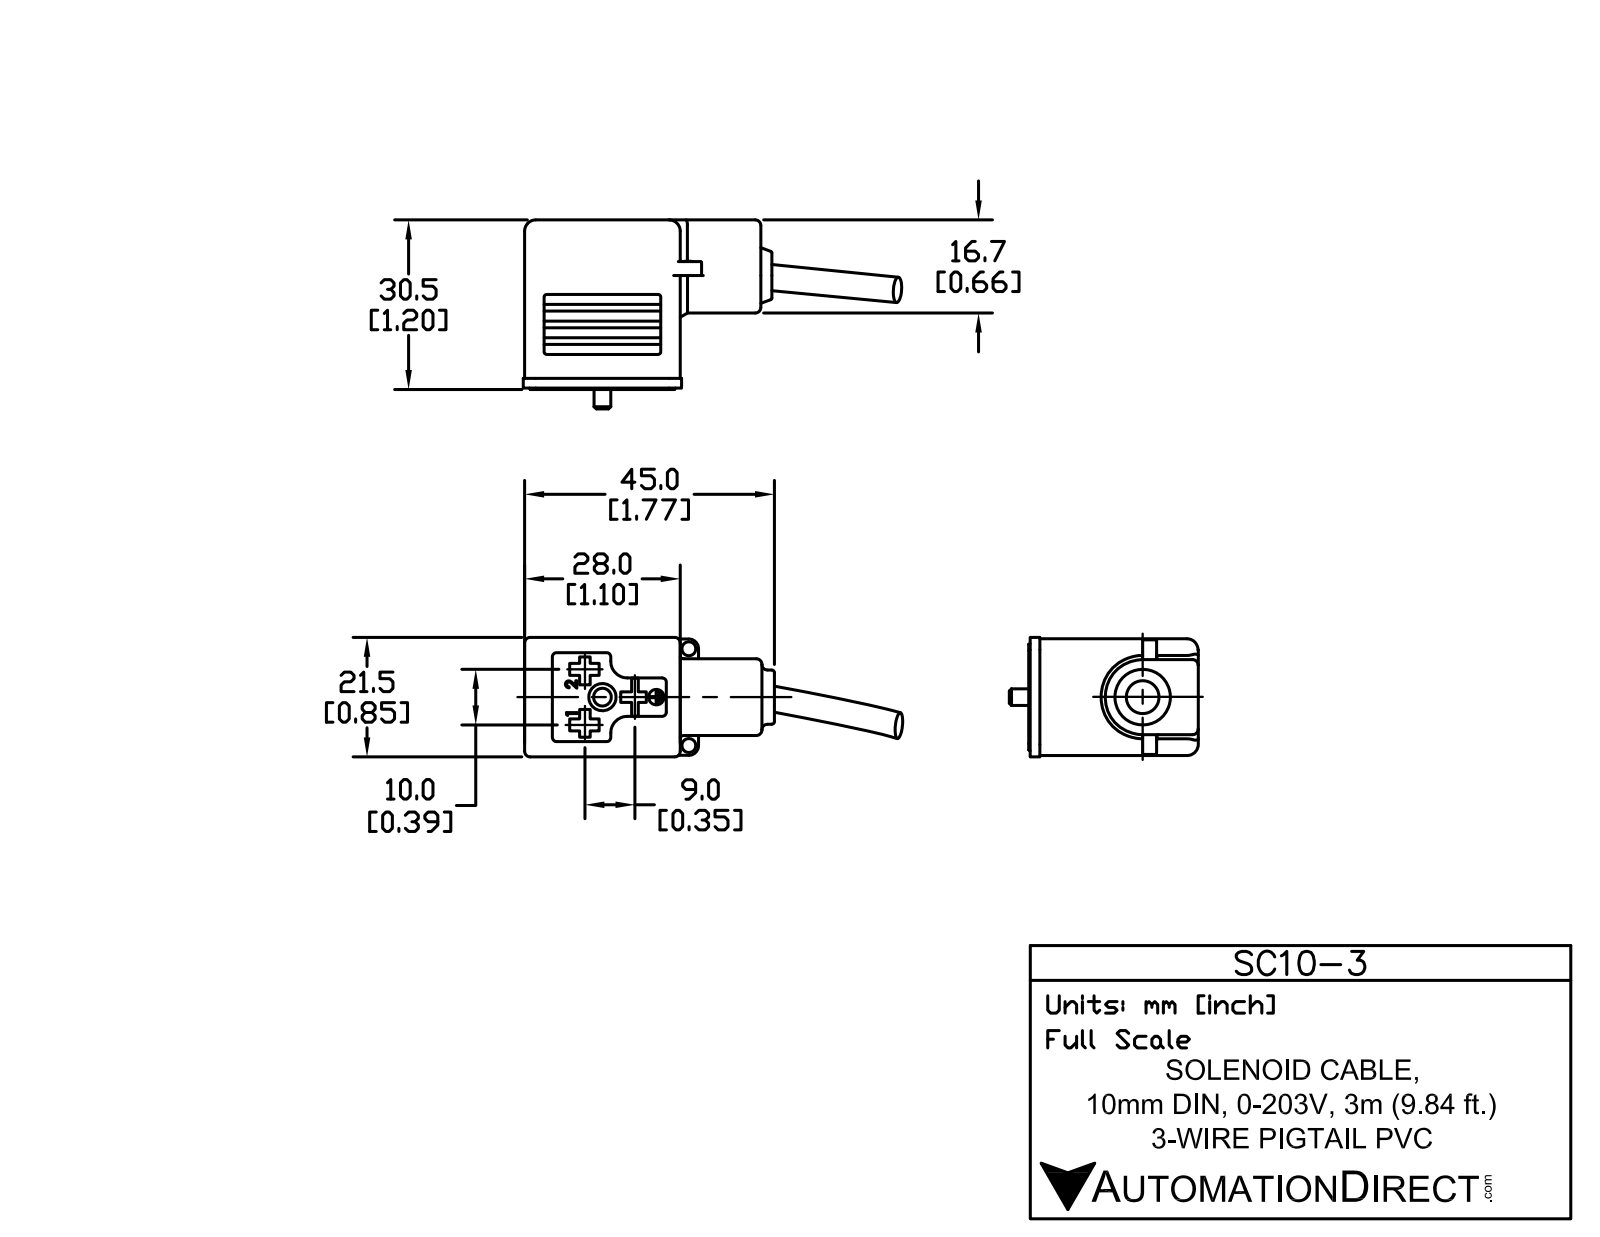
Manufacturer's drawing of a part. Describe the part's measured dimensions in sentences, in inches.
The part is named "SC10-3". Its 3-D file was written by "SolidWorks 2011 (AUTOMOTIVE_DESIGN)". It is 2 solids with 202 faces: 130 planar, 45 cylindrical and 27 other. Overall it measures 2.668 by 1.35 by 0.846 inches. Its volume is 1.213 cubic inches and its surface area 10.52 square inches. Round holes: 2 of diameter 0.098, 1 of diameter 0.109, 1 of diameter 0.126, 1 of diameter 0.193, 1 of diameter 0.22, 1 of diameter 0.26. Round bosses or shafts: 1 of diameter 0.384, 1 of diameter 0.256, 1 of diameter 0.108. Partial cylindrical surfaces (rounded edges, fillets, slot ends): 19 of radius 0.039, 6 of radius 0.03, 2 of radius 0.069, 2 of radius 0.118, 1 of radius 0.272. The main face-to-face distances are 0.823, 1.181, 1.079, 0.14, 1.102, 0.079, 0.683, 1.1, 1.179, 0.543. The hole center spacings are 0.413, 0.702, 0.382, 0.685.
